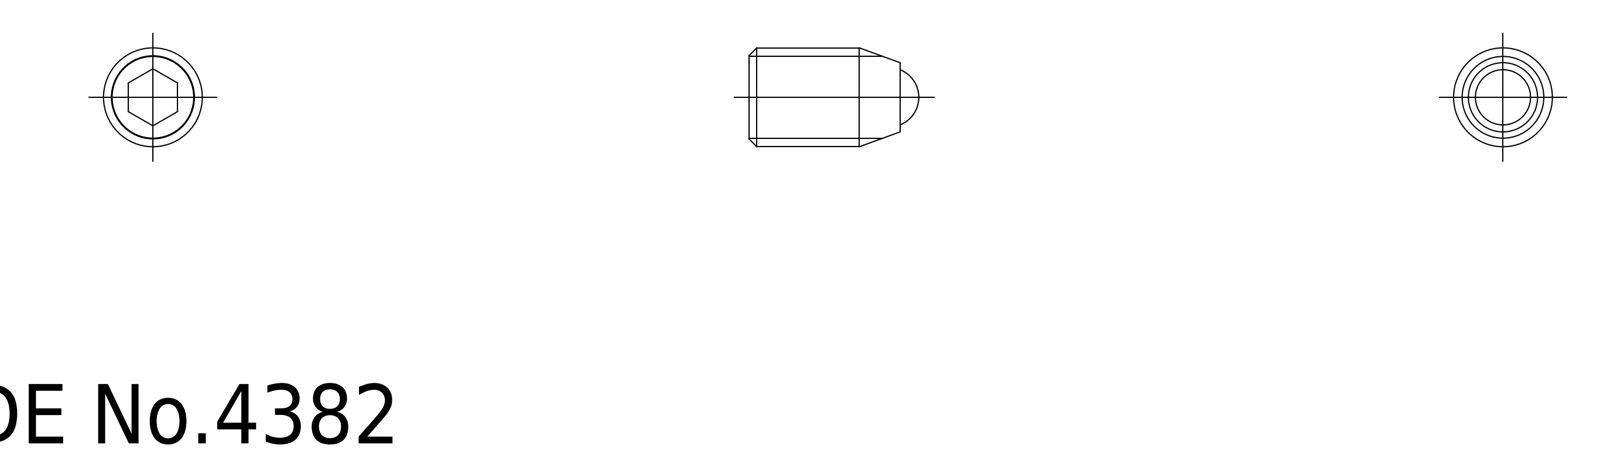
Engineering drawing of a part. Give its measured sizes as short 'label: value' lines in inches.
name: ball; SCS_M5_8_R_17179_36
written by: CADfix (AUTOMOTIVE_DESIGN)
unit: in
bodies: 2 solids, 20 faces (0 planar, 0 cylindrical, 20 other)
size: 0.339 × 0.197 × 0.197
volume: 0.007 in³; area: 0.355 in²
